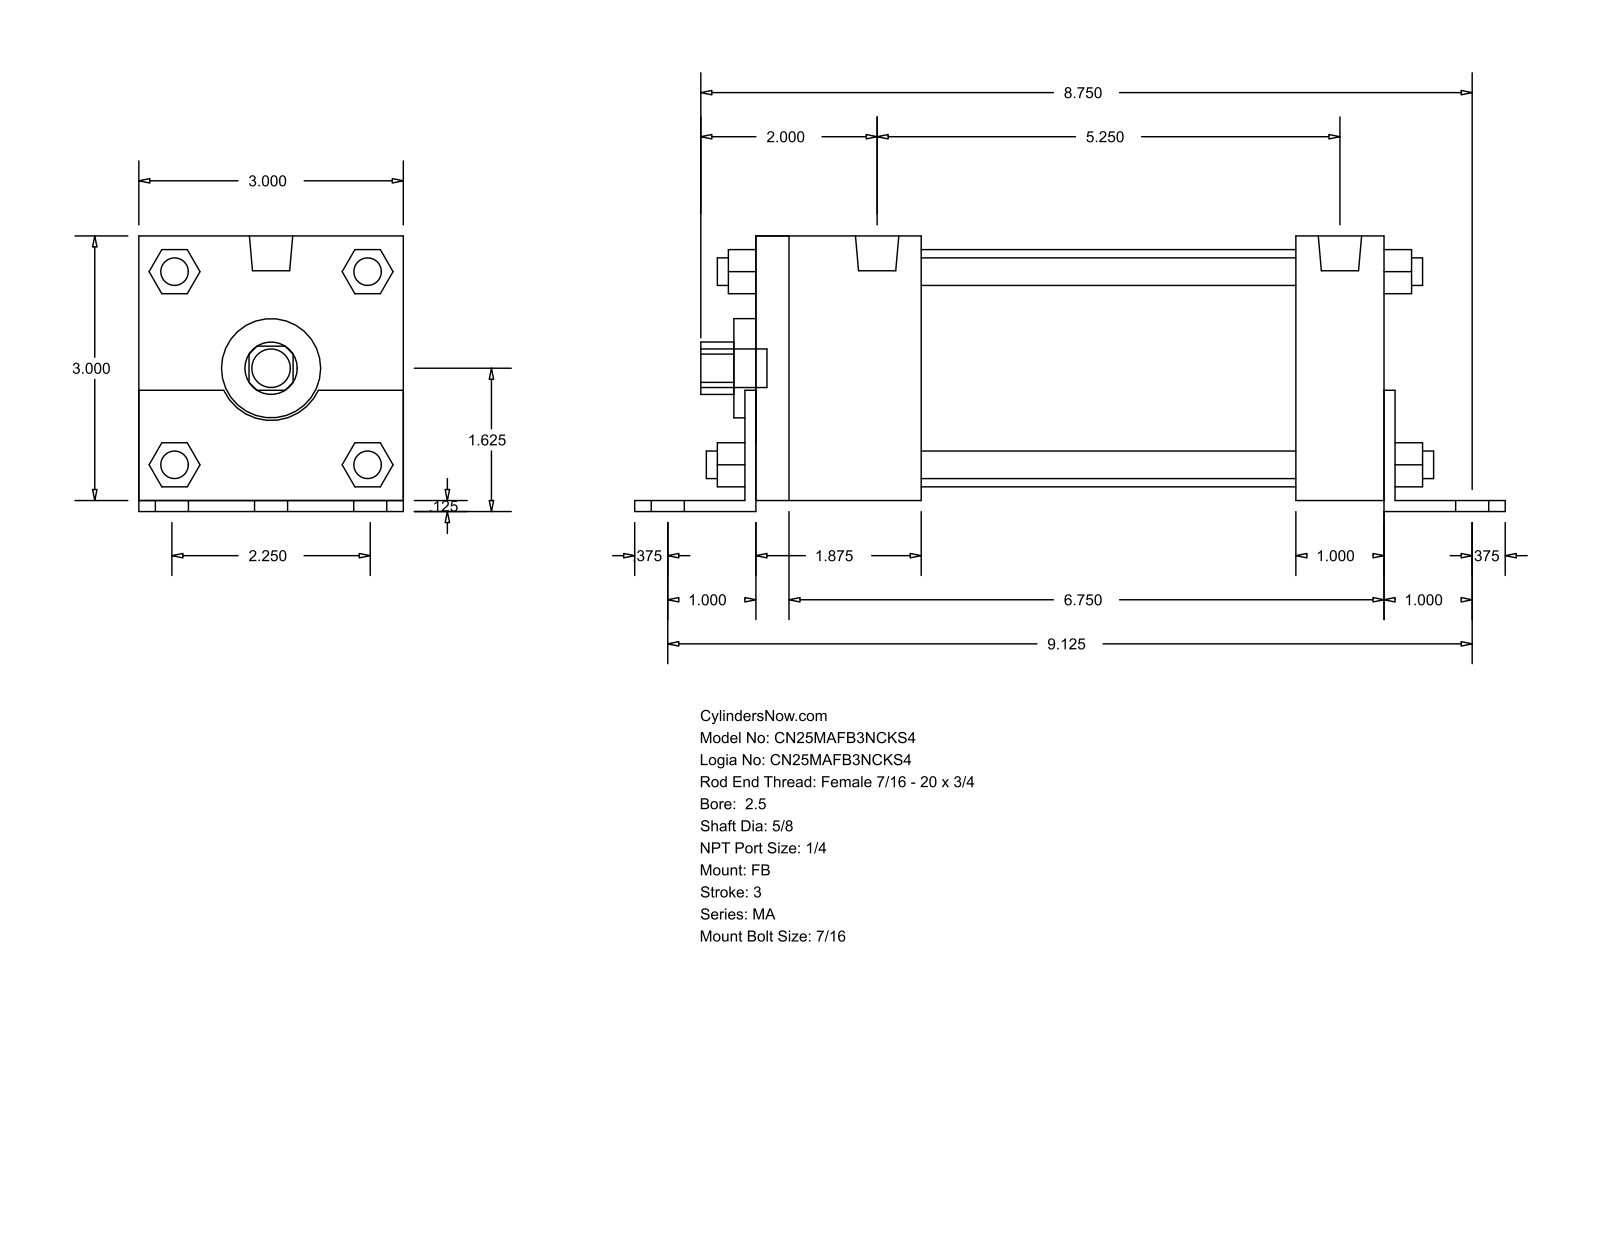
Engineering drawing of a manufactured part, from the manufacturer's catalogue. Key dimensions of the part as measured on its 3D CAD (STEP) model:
Part name (STEP PRODUCT): MA_FB__0250_0.625
STEP written by: GSSL Pune (CONFIG_CONTROL_DESIGN)
Units: millimetres
Bodies: 0 solids, 140 faces (105 planar, 35 cylindrical, 0 other)
Overall size (bounding box): 250.82 × 79.38 × 76.2
Round holes (diameter × count): ⌀15.88 ×1, ⌀28.57 ×1, ⌀68.33 ×1
Round bosses / shafts (diameter × count): ⌀7.94 ×8, ⌀11.11 ×7, ⌀12.49 ×2
Partial cylindrical surfaces — rounded edges, fillets, slot ends (radius × count): R7.54 ×1, R15.05 ×1
Main face-to-face distances: 76.2, 3.17, 79.37, 3.18, 184.15, 180.97, 28.58, 47.62, 25.4, 187.33
